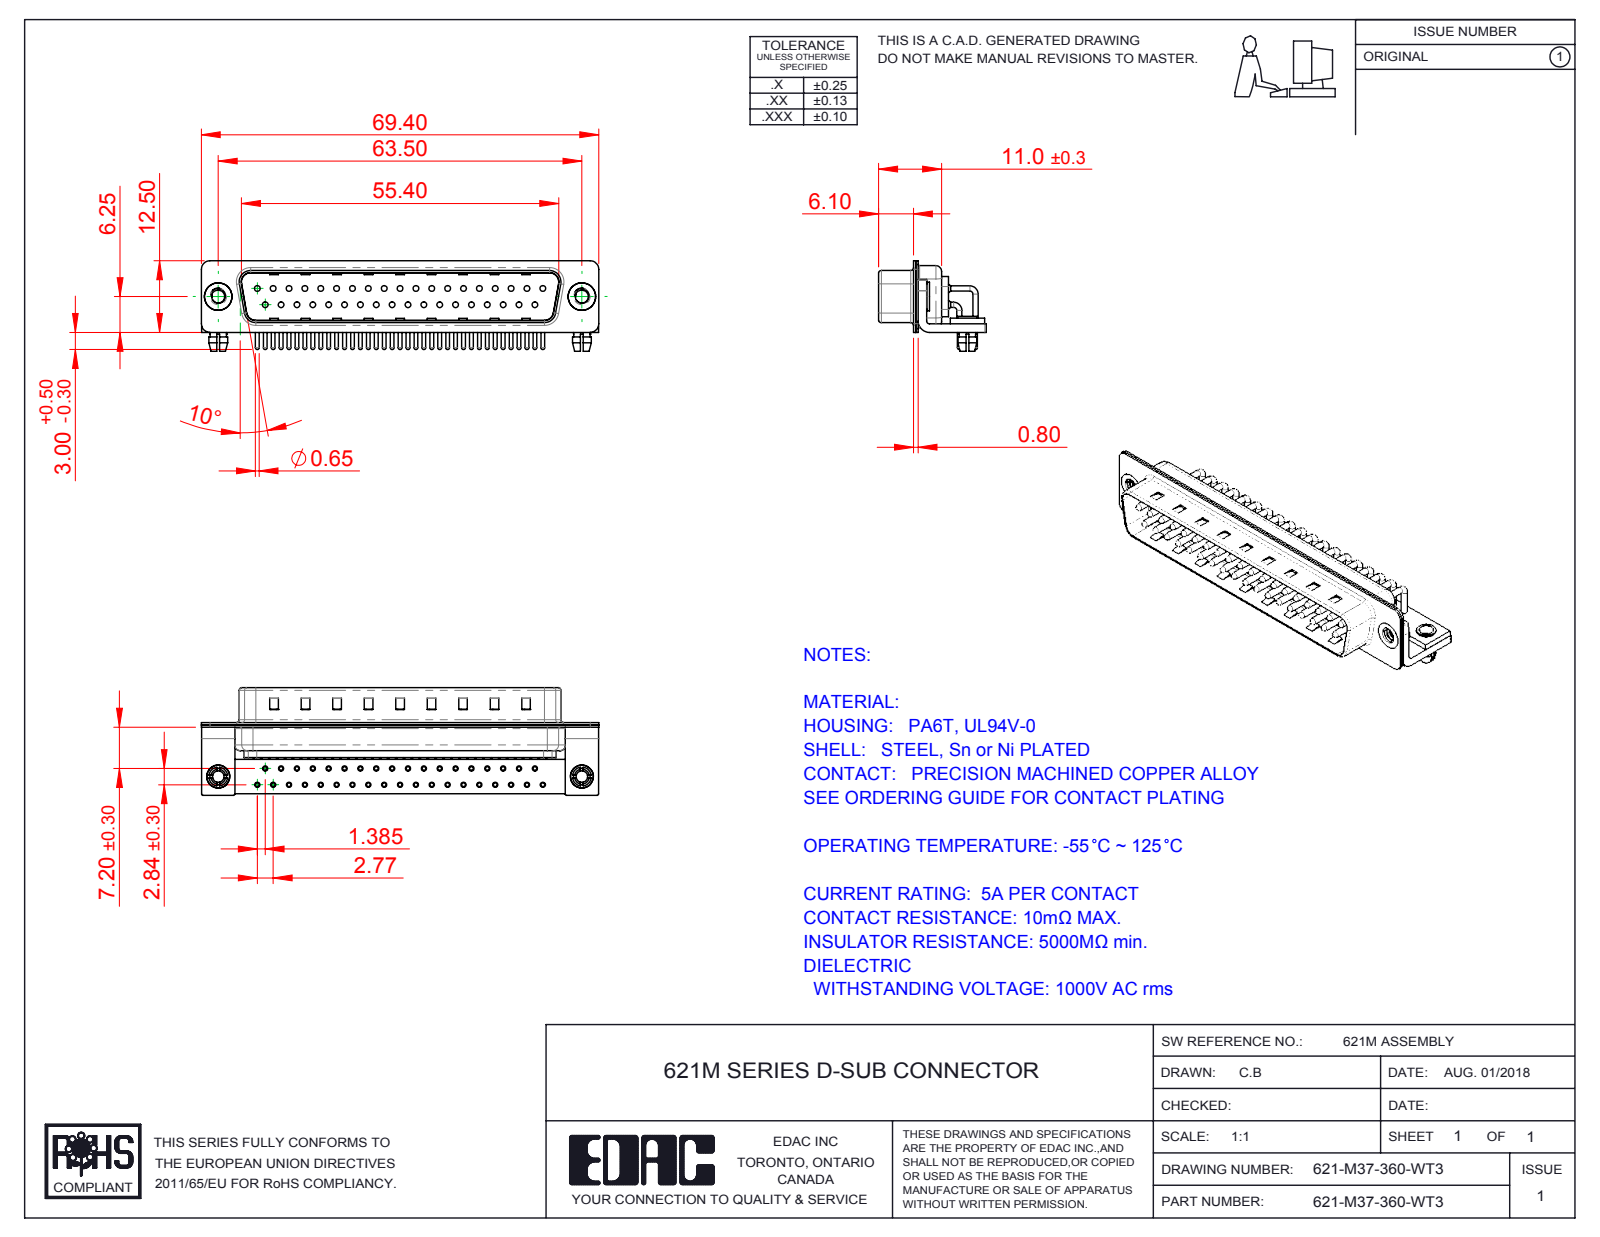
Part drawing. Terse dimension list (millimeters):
name: 621-M37-360-WT3; 621M Board Lock; 621M Stabilizer Board_37 Contacts; 621M Stabilizer Bracket (+6 more)
written by: SolidWorks 2016 (CONFIG_CONTROL_DESIGN)
unit: mm
bodies: 47 solids, 4698 faces (2645 planar, 1601 cylindrical, 452 other)
size: 69.4 × 18.8 × 15.8
volume: 4 643 mm³; area: 12 155 mm²
holes: 39× ⌀2, 37× ⌀0.9, 37× ⌀1, 37× ⌀1.7, 2× ⌀2.26, 2× ⌀2.5, 2× ⌀3.2, 2× ⌀4, 2× ⌀4.8
bosses: 46× ⌀0.9, 37× ⌀1.5, 37× ⌀0.65, 2× ⌀5, 2× ⌀4.9, 2× ⌀4, 2× ⌀3.4, 2× ⌀3.3
rounds: 37× R1.01, 16× R0.25, 16× R1.5, 13× R2, 9× R0.5, 8× R1.6, 4× R0.6, 4× R0.65
face distances: 0.4, 0.85, 1.25, 9.55, 1.5, 10.4, 8.3, 0.8, 8.7, 1
hole spacings: 3.16, 2.77, 5.54, 8.31, 11.08, 13.85, 5.03, 16.62
